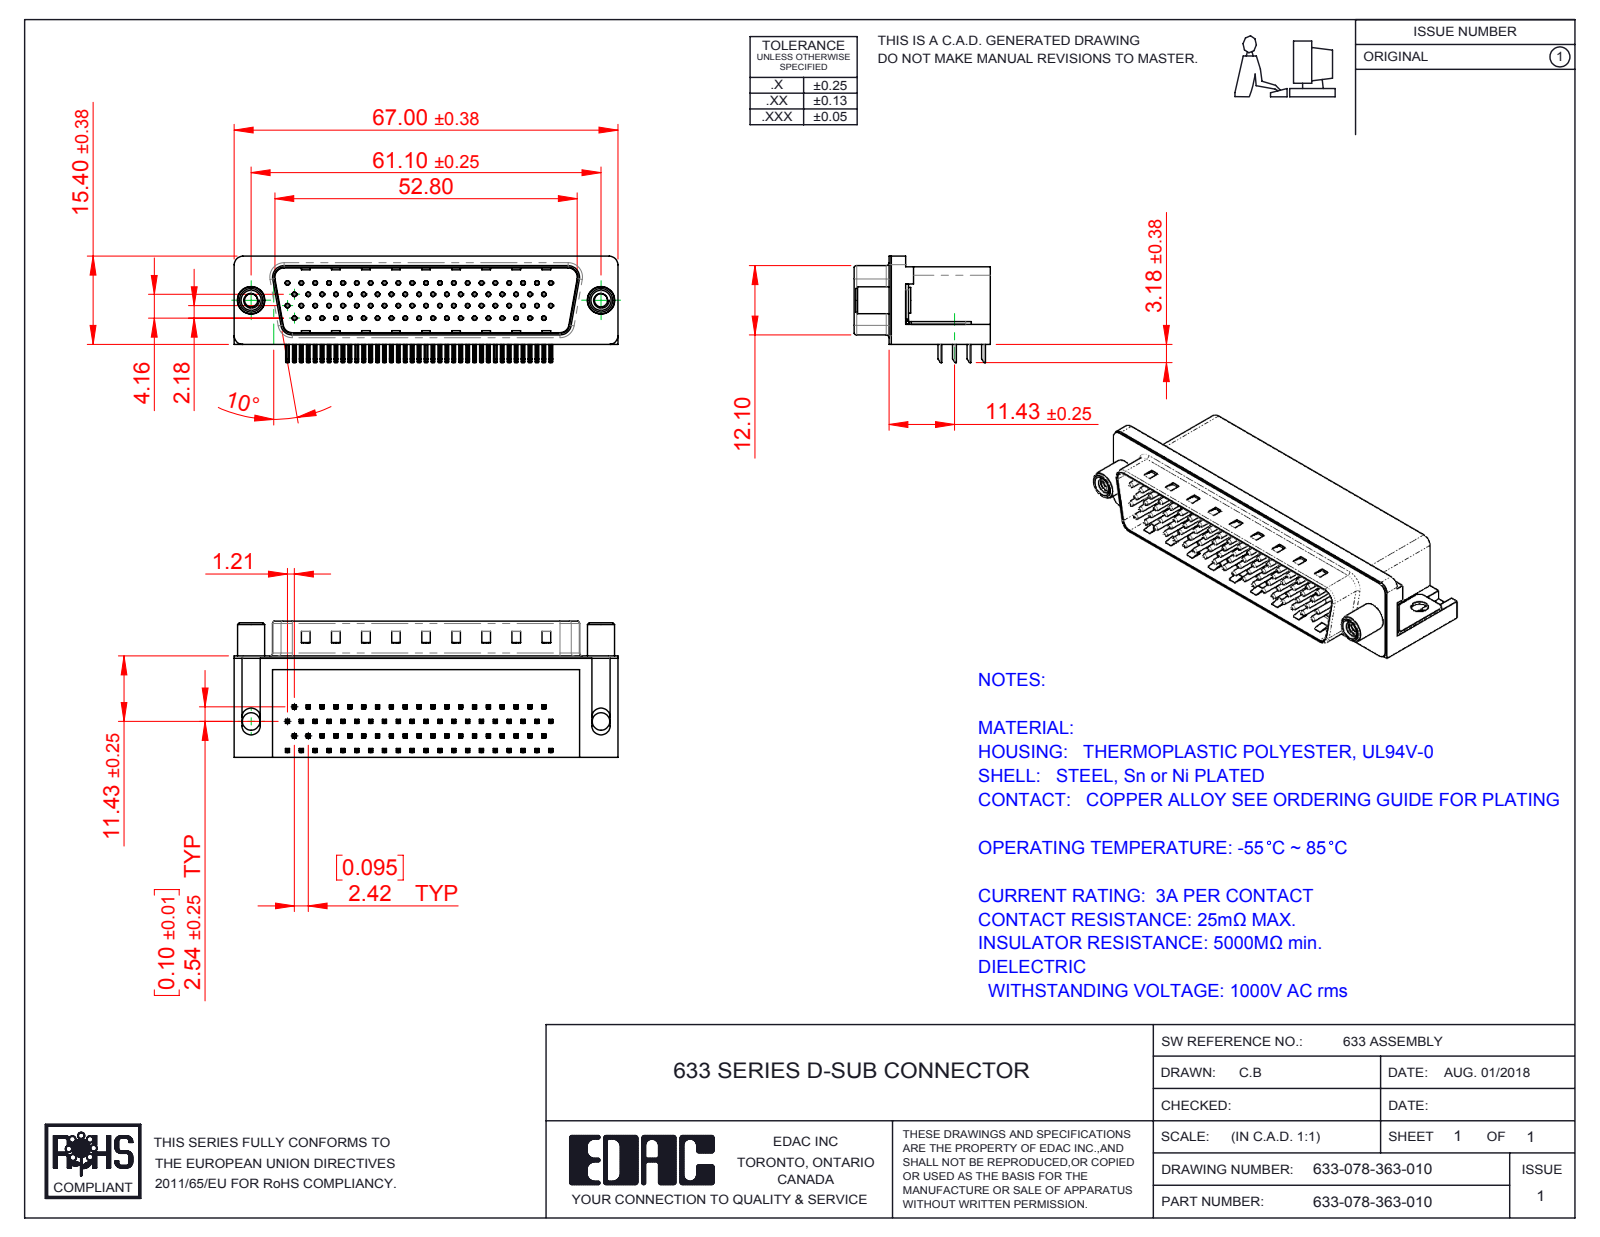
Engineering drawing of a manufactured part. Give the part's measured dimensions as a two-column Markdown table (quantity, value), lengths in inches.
| quantity | value |
| --- | --- |
| part name | 633 Contact Bottom_78 Contact; 633 Thru Hole Board Mount_78 Contact; 633 Contact Top_78 Contact; 633 Contact Top 78 (+5 more) |
| STEP written by | SolidWorks 2016 (CONFIG_CONTROL_DESIGN) |
| units | inches |
| bodies | 84 solids, 6268 faces (3971 planar, 1786 cylindrical, 511 other) |
| overall size | 2.638 × 0.937 × 0.731 |
| volume | 0.897 in³ |
| surface area | 25.63 in² |
| round holes (diameter × count) | 0.014 × 78, 0.031 × 78, 0.091 × 2, 0.12 × 2, 0.122 × 2, 0.157 × 2, 0.189 × 2, 0.197 × 2 |
| round bosses / shafts (diameter × count) | 0.03 × 78, 0.193 × 2, 0.185 × 2, 0.177 × 2, 0.152 × 2 |
| partial cylindrical surfaces (radius × count) | 0.01 × 312, 0.005 × 156, 0.039 × 16, 0.02 × 9, 0.063 × 8, 0.059 × 6, 0.018 × 4, 0.035 × 4 |
| main face-to-face distances | 0.016, 0.52, 0.681, 0.461, 0.526, 0.081, 0.541, 0.065, 0.073, 0.469 |
| hole center spacings | 0.095, 0.191, 0.286, 0.381, 0.246, 0.281, 0.476, 0.339 |
